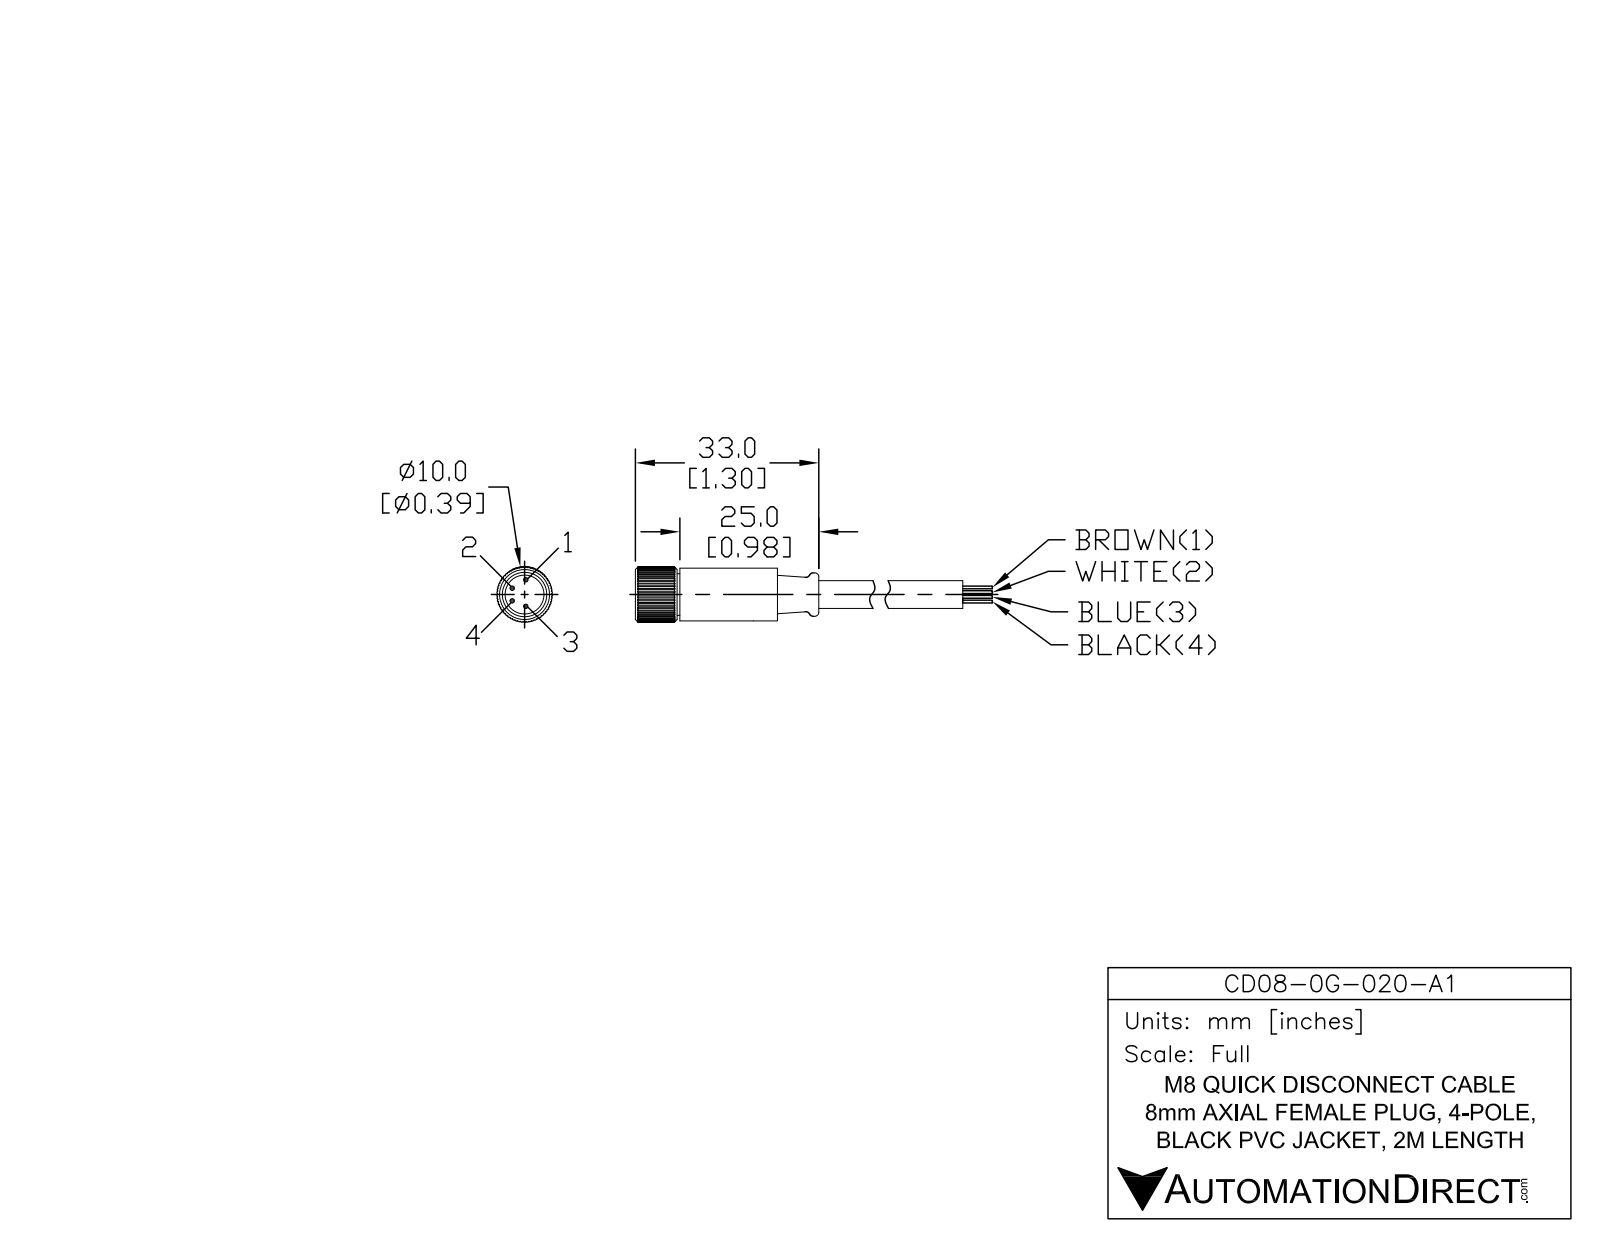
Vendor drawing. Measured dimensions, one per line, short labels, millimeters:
name: CD08-0G-020-A1
written by: SolidWorks 2017 (AUTOMOTIVE_DESIGN)
unit: mm
bodies: 4 solids, 303 faces (214 planar, 85 cylindrical, 4 other)
size: 134.6 × 10 × 10
volume: 4 237 mm³; area: 3 314 mm²
holes: 4× ⌀0.9, 1× ⌀7.2, 1× ⌀8
bosses: 1× ⌀10, 1× ⌀7, 1× ⌀4.8
face distances: 26.9, 34.6, 7.7, 0.6, 9, 34, 7.1, 100, 126.9, 134
hole spacings: 2.41, 2.48, 2.71, 4.29, 2.3, 4.8
